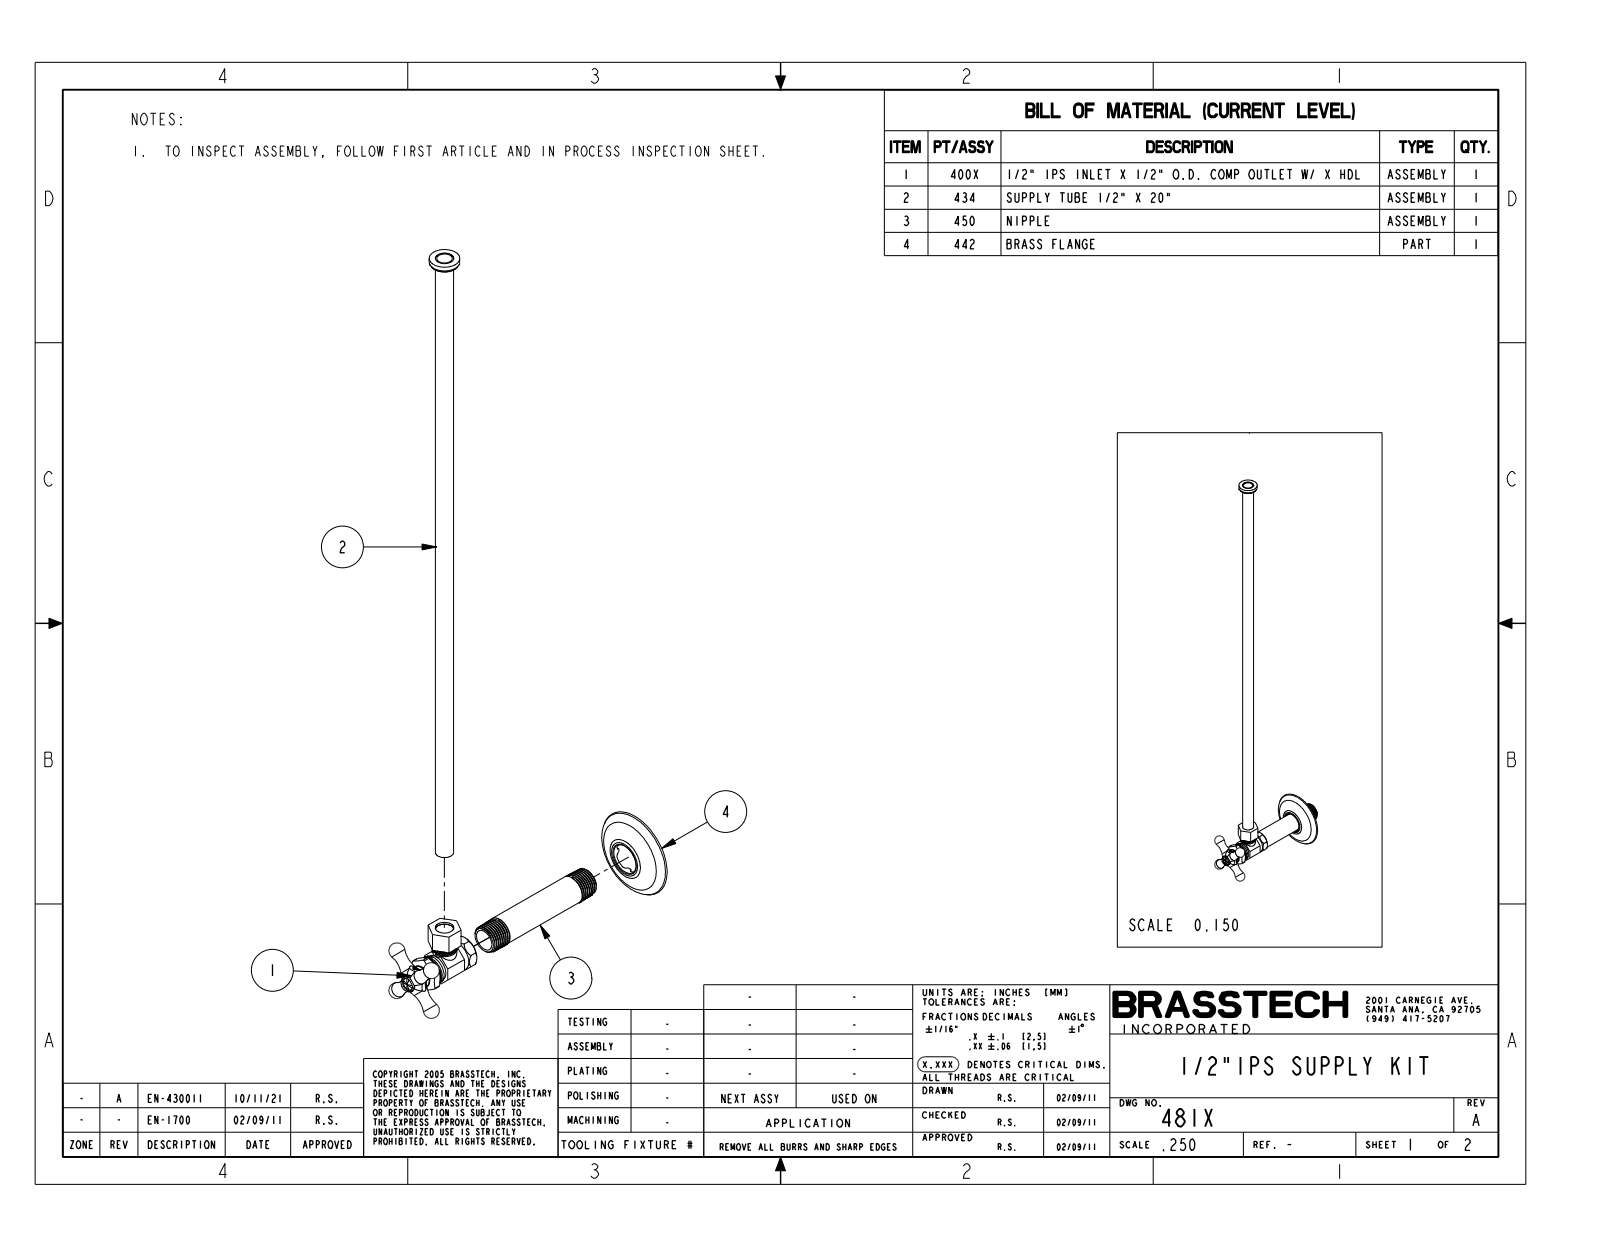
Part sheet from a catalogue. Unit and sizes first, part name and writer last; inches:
Units: inches
Overall size (bounding box): 21.605 × 5.574 × 2.5
Round holes (diameter × count): ⌀0.13 ×1, ⌀0.25 ×1, ⌀0.375 ×1, ⌀0.4 ×1, ⌀0.428 ×1, ⌀0.464 ×1, ⌀0.48 ×1, ⌀0.594 ×1, ⌀0.64 ×1, ⌀0.687 ×1, ⌀0.75 ×1, ⌀0.813 ×1
Round bosses / shafts (diameter × count): ⌀0.86 ×1, ⌀0.84 ×1, ⌀0.811 ×1, ⌀0.78 ×1, ⌀0.68 ×1, ⌀0.629 ×1, ⌀0.62 ×1, ⌀0.595 ×1
Partial cylindrical surfaces — rounded edges, fillets, slot ends (radius × count): R0.01 ×18, R0.05 ×6, R0.15 ×4, R0.082 ×1, R0.17 ×1, R0.376 ×1
Main face-to-face distances: 0.812, 0.9, 0.044, 0.856, 0.53, 0.875, 19.693, 19.163, 1.113, 1.643
Hole centre spacings: 1.113
Volume: 3.847 in³ · Surface area: 128.6 in²
Bodies: 3 solids, 792 faces (246 planar, 224 cylindrical, 322 other)
Part name (STEP PRODUCT): 481X
STEP written by: CREO PARAMETRIC BY PTC INC, 2018500 (CONFIG_CONTROL_DESIGN)
